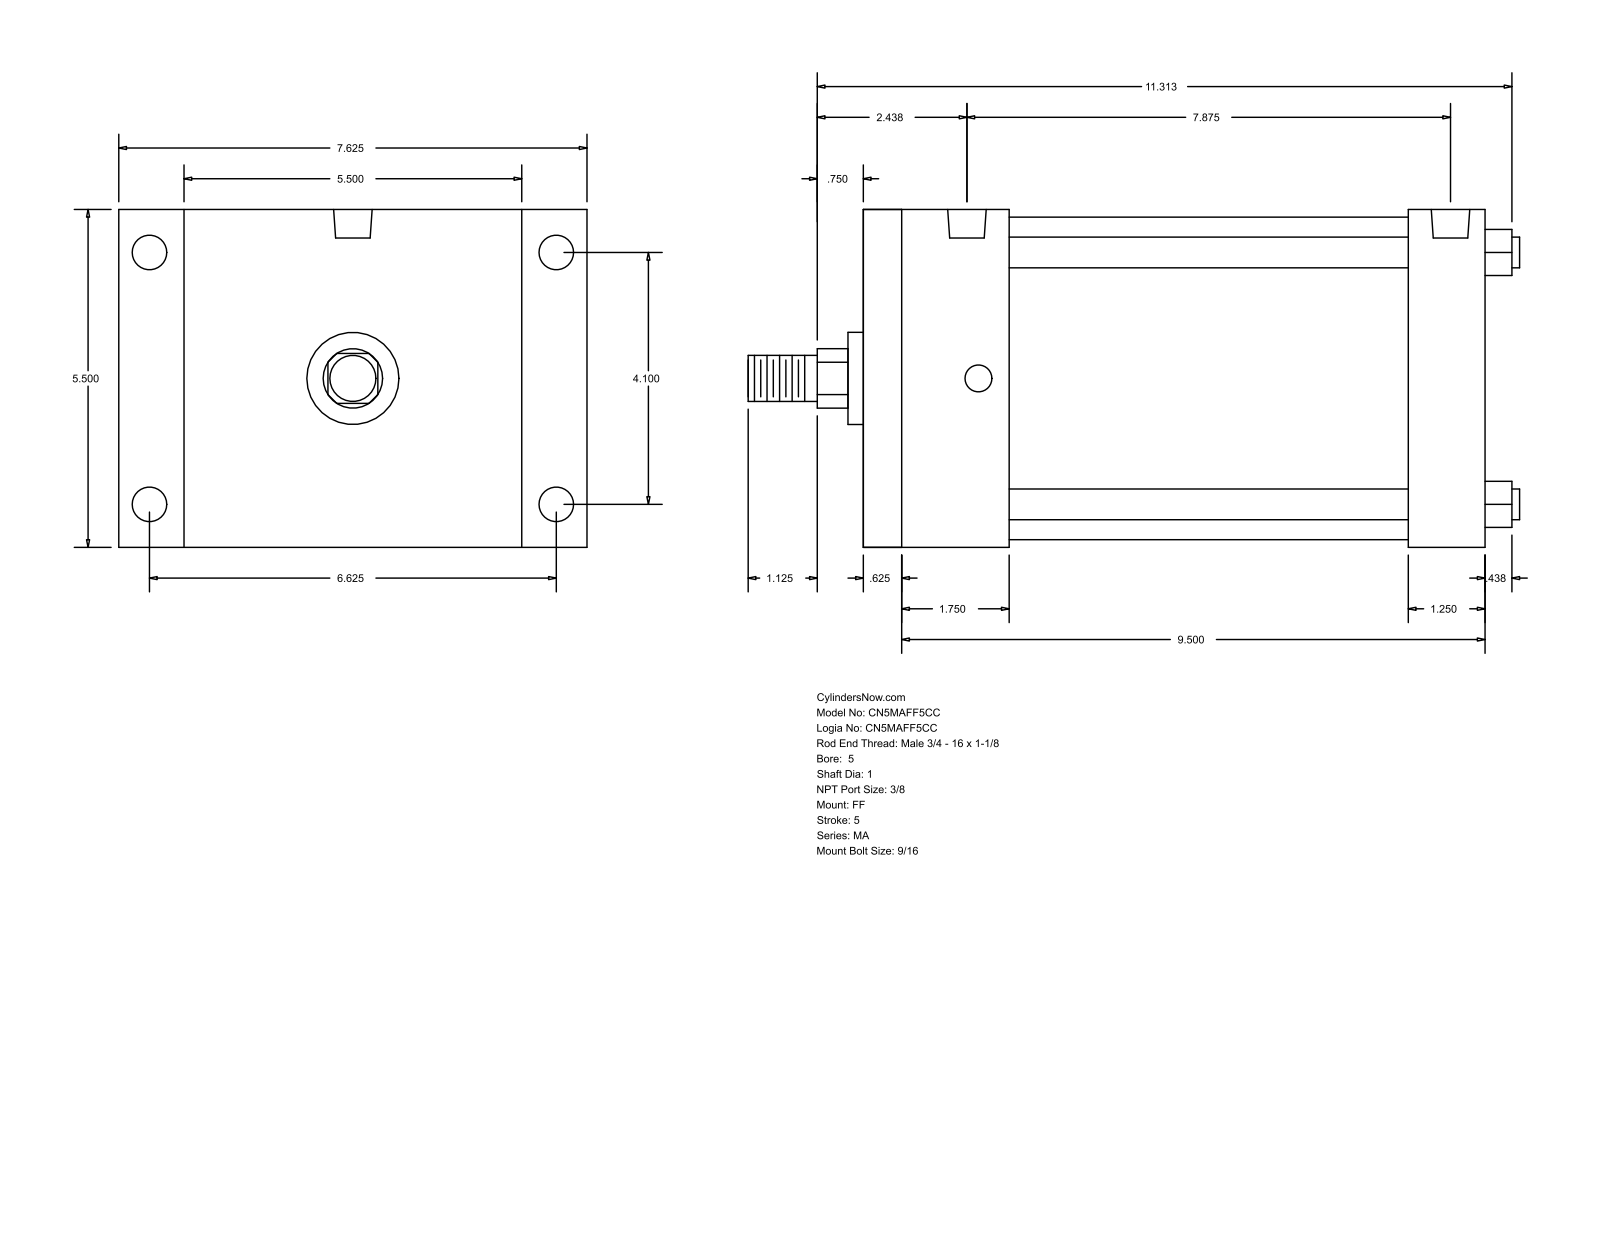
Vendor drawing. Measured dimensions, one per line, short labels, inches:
name: MA_FF__0500_1
written by: GSSL Pune (CONFIG_CONTROL_DESIGN)
unit: in
bodies: 0 solids, 92 faces (64 planar, 28 cylindrical, 0 other)
size: 12.563 × 7.625 × 5.5
holes: 4× ⌀0.437, 4× ⌀0.563, 2× ⌀0.627
bosses: 4× ⌀0.5, 1× ⌀5.25, 1× ⌀1.5, 1× ⌀1, 1× ⌀0.75
rounds: 1× R0.484
face distances: 5.5, 10.125, 0.625, 9.5, 6.5, 8.875, 8.25, 1.25, 2.375, 1.75
hole spacings: 0.187, 4.1, 6.625, 7.5, 7.688, 7.791, 7.875
